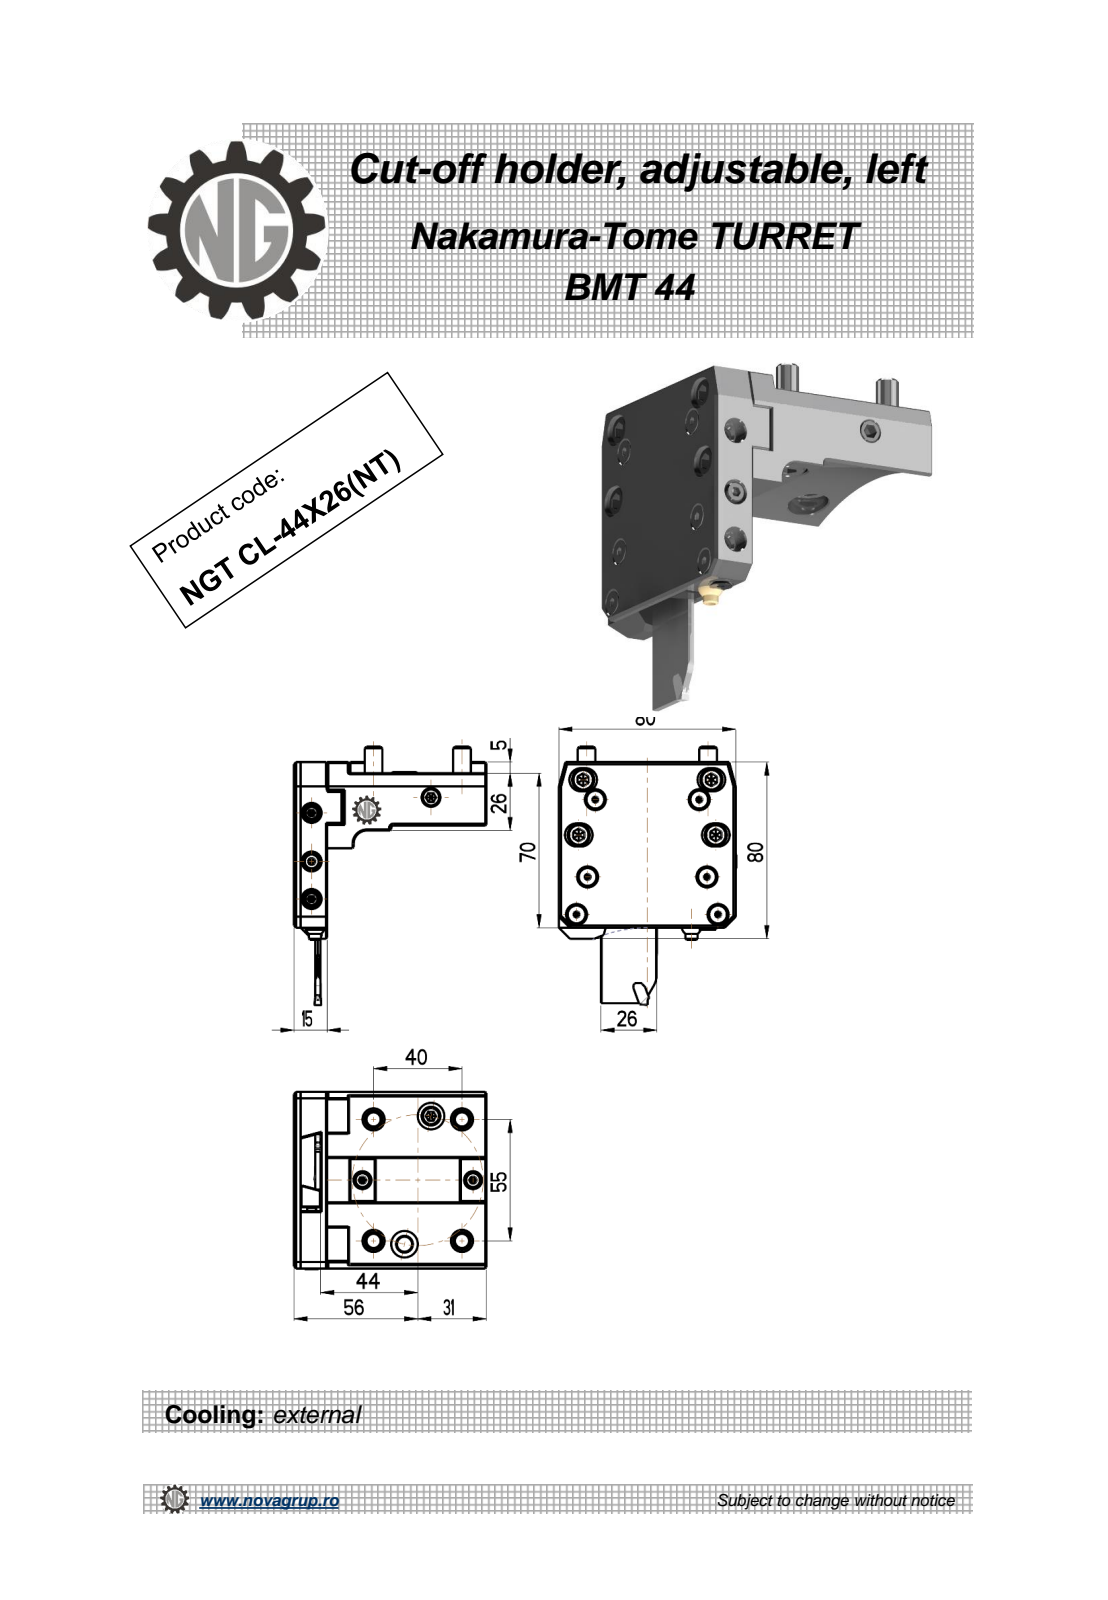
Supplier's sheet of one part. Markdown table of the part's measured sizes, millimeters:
| quantity | value |
| --- | --- |
| part name | NGT_CL_44_26_NT |
| STEP written by | PRO/ENGINEER BY PARAMETRIC TECHNOLOGY CORPORATION, 2010280 (CONFIG_CONTROL_DESIGN) |
| units | millimeters |
| bodies | 1 solid, 486 faces (295 planar, 110 cylindrical, 81 other) |
| overall size | 87.45 × 87 × 80.26 |
| volume | 199 600 mm³ |
| surface area | 47 927 mm² |
| round holes (diameter × count) | 5 × 2, 8 × 2, 12 × 2, 3.5 × 1, 6.8 × 1 |
| round bosses / shafts (diameter × count) | 8 × 5, 10 × 4, 4 × 3, 5.5 × 1 |
| partial cylindrical surfaces (radius × count) | 0.2 × 24, 0.31 × 12, 5.25 × 8, 0.14 × 6, 0.16 × 6, 0.41 × 6, 1 × 1, 6 × 1 |
| main face-to-face distances | 3, 12, 15, 5, 10, 80, 9, 75, 22, 26 |
| hole center spacings | 39, 41.49, 59.23, 71.81 |
